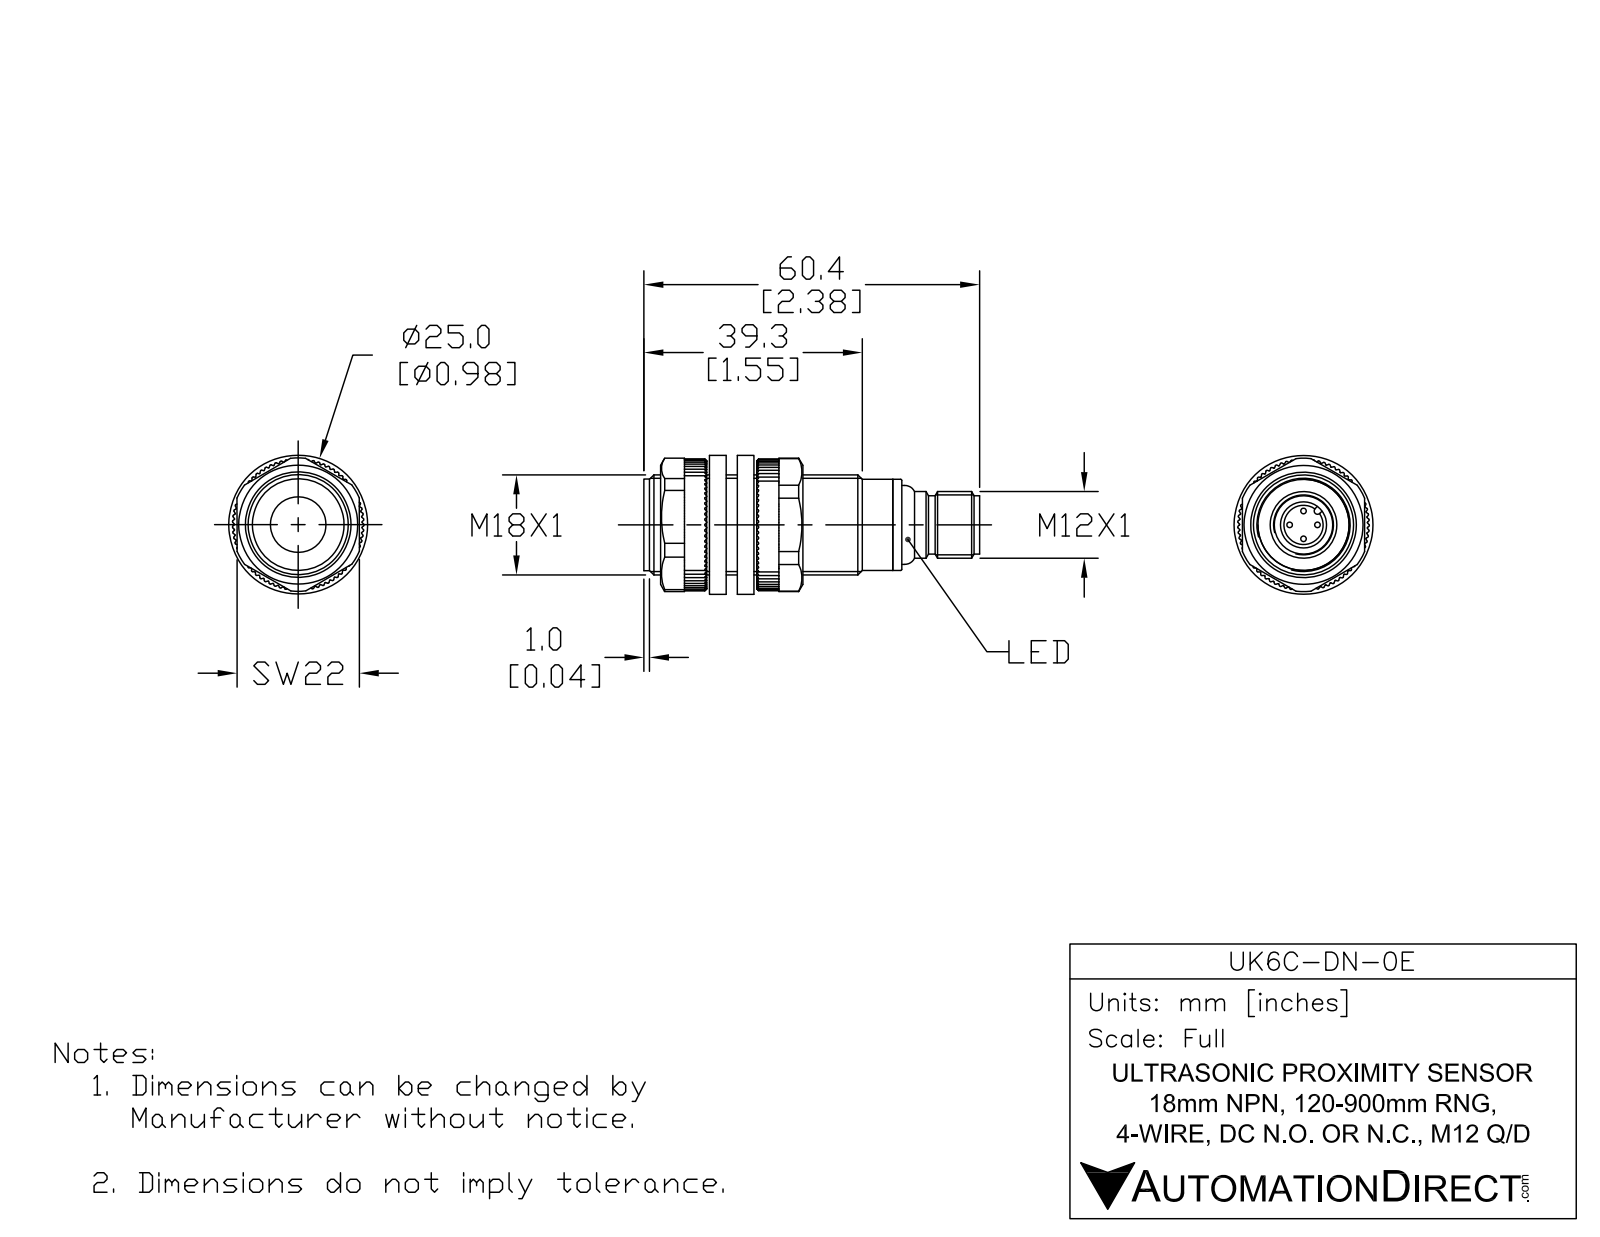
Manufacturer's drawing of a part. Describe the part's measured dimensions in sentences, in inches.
The part is named "UK6C-DN-0E". Its 3-D file was written by "SolidWorks 2017 (AUTOMOTIVE_DESIGN)". It is 4 solids with 86 faces: 15 planar, 36 cylindrical and 35 other. Overall it measures 2.374 by 0.709 by 0.709 inches. Its volume is 0.759 cubic inches and its surface area 7.648 square inches. Round holes: 1 of diameter 0.276, 1 of diameter 0.327, 1 of diameter 0.374. Round bosses or shafts: 4 of diameter 0.039, 1 of diameter 0.709, 1 of diameter 0.646, 1 of diameter 0.622, 1 of diameter 0.559, 1 of diameter 0.472, 1 of diameter 0.413. Partial cylindrical surfaces (rounded edges, fillets, slot ends): 1 of radius 0.024. The main face-to-face distances are 1.724, 0.039, 1.764, 0.039, 1.763, 1.823, 1.822, 1.783, 0.059, 2.024.
